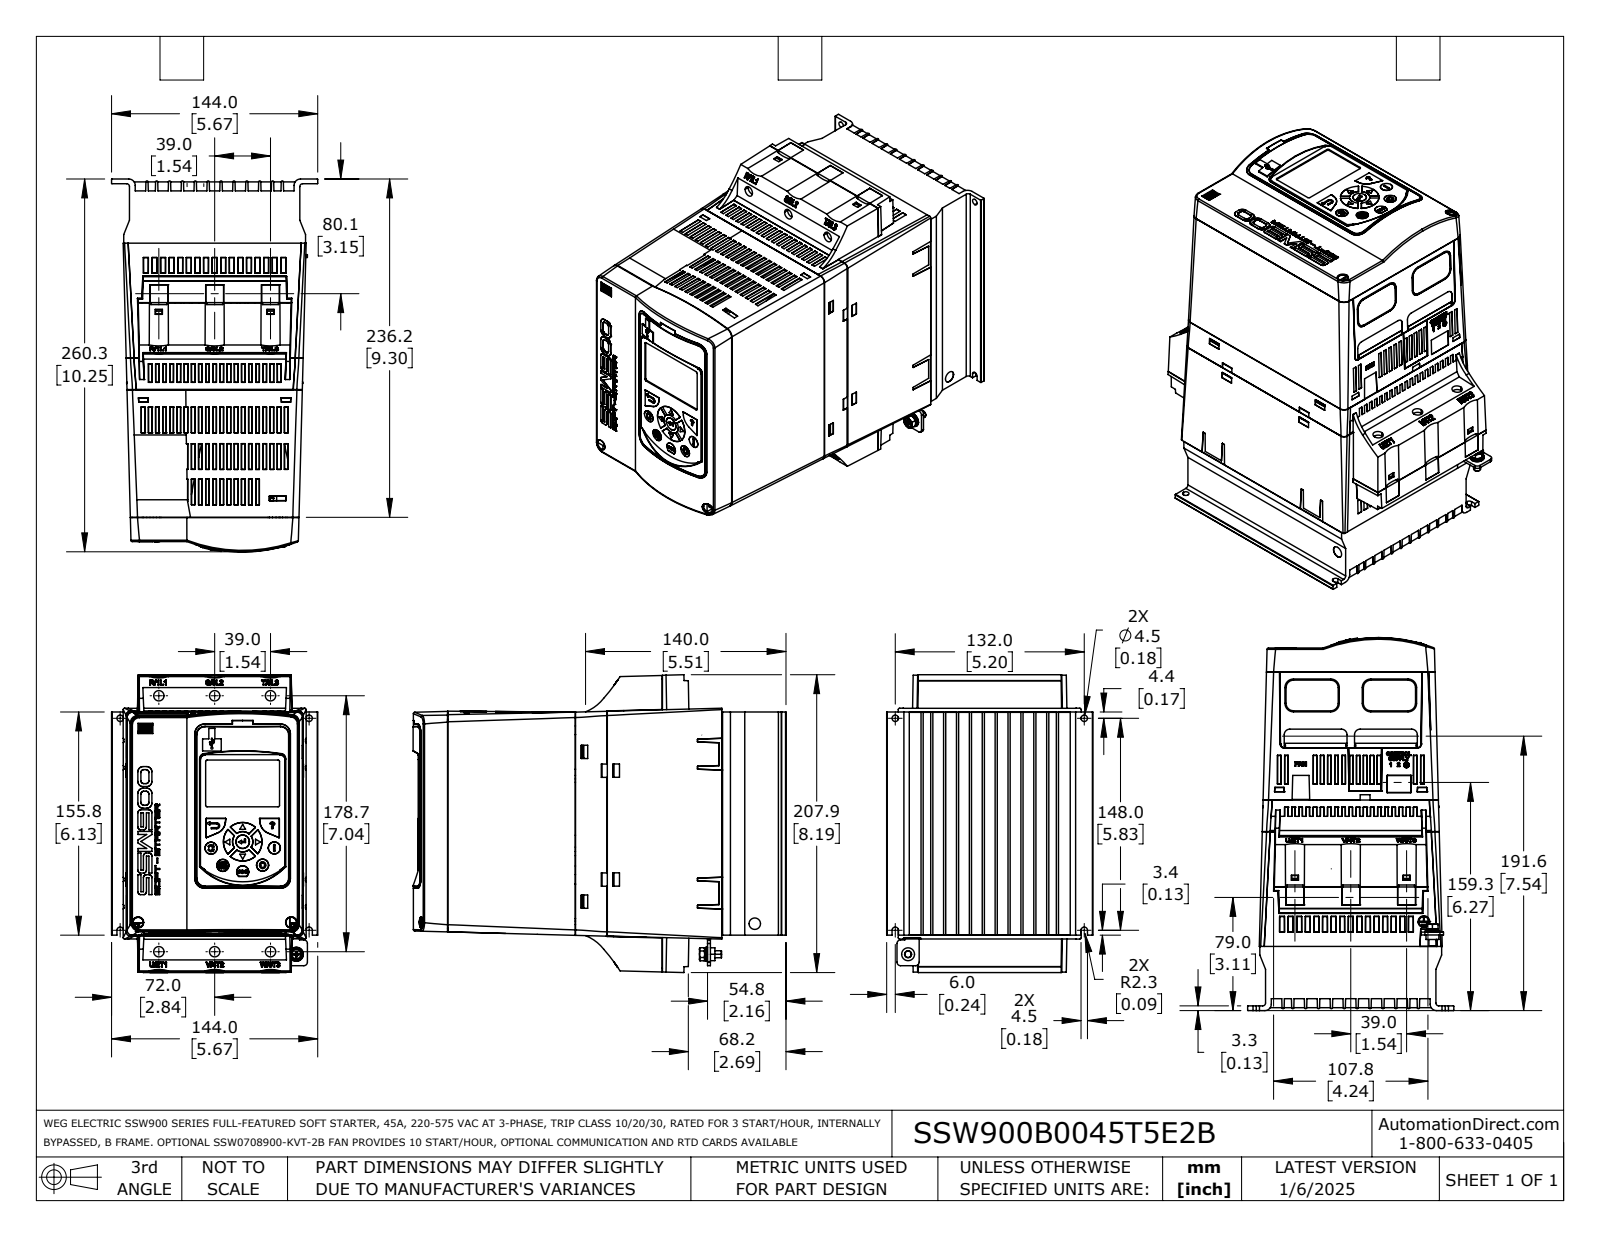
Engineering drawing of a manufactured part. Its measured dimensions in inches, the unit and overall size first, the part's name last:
Units: inches
Overall size (bounding box): 10.254 × 8.187 × 5.669
Round holes (diameter × count): ⌀0.283 ×6, ⌀0.177 ×2, ⌀0.118 ×1, ⌀0.133 ×1, ⌀0.165 ×1, ⌀0.248 ×1, ⌀0.277 ×1, ⌀0.285 ×1, ⌀0.315 ×1
Round bosses / shafts (diameter × count): ⌀0.387 ×1, ⌀0.354 ×1, ⌀0.323 ×1, ⌀0.317 ×1, ⌀0.264 ×1, ⌀0.197 ×1, ⌀0.193 ×1, ⌀0.151 ×1
Partial cylindrical surfaces — rounded edges, fillets, slot ends (radius × count): R0.012 ×28, R0.008 ×16, R0.03 ×12, R0.02 ×9, R0.006 ×7, R0.017 ×4, R0.039 ×4, R0.098 ×4
Main face-to-face distances: 5.707, 5.715, 9.887, 4.179, 4.171, 0.098, 6.134, 7.007, 0.7, 0.783
Hole centre spacings: 1.535, 7.201, 7.035, 3.071, 7.676, 0.713, 0.886, 0.985
Volume: 310.3 in³ · Surface area: 437 in²
Bodies: 6 solids, 3794 faces (2929 planar, 209 cylindrical, 656 other)
Part name (STEP PRODUCT): SSW900B0045T5E2B
STEP written by: SolidWorks 2021 (AUTOMOTIVE_DESIGN)
